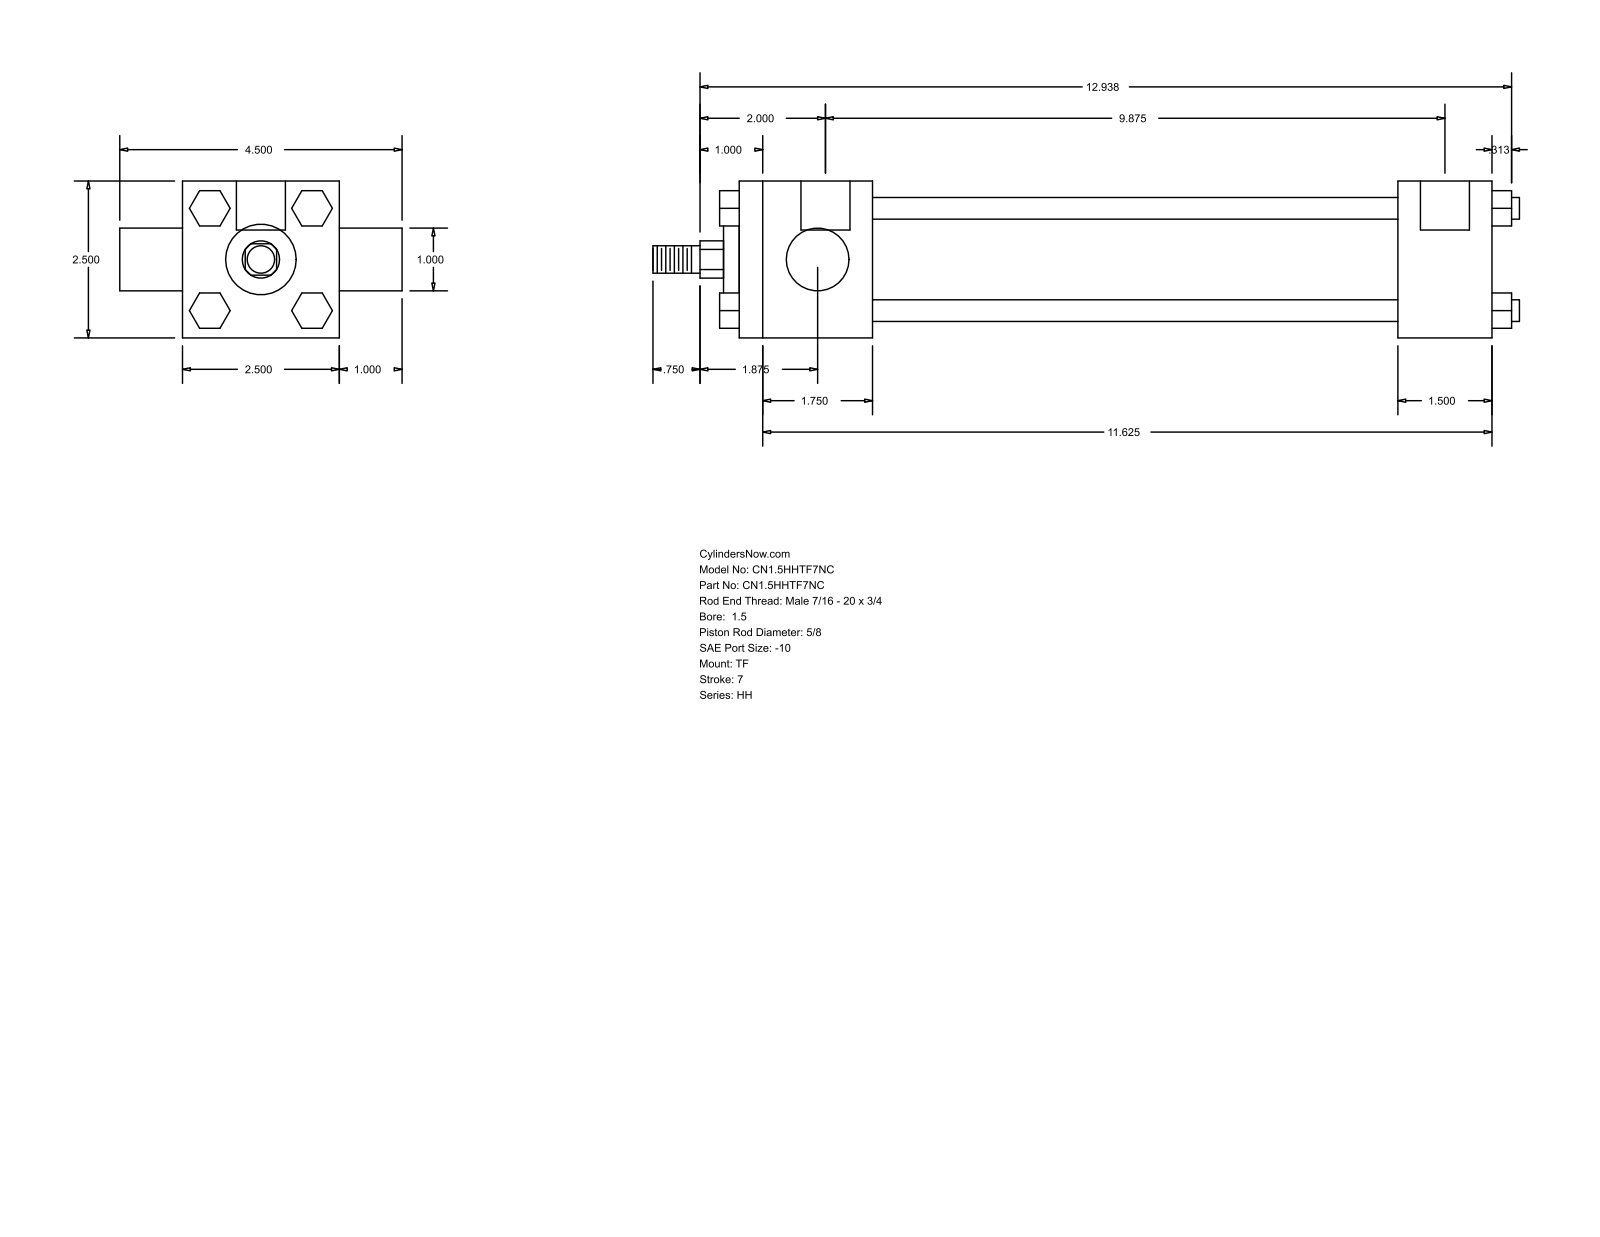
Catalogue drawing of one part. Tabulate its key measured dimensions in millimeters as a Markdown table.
| quantity | value |
| --- | --- |
| part name | HH_TF__0150_0.625 |
| STEP written by | GSSL Pune (CONFIG_CONTROL_DESIGN) |
| units | millimeters |
| bodies | 0 solids, 120 faces (92 planar, 28 cylindrical, 0 other) |
| overall size | 350.84 × 114.3 × 63.5 |
| round holes (diameter × count) | 5.56 × 3, 19.84 × 2 |
| round bosses / shafts (diameter × count) | 8.76 × 4, 44.45 × 1, 28.57 × 1, 25.4 × 1, 15.88 × 1, 11.11 × 1 |
| partial cylindrical surfaces (radius × count) | 7.54 × 1 |
| main face-to-face distances | 63.5, 304.8, 53.97, 250.83, 266.69, 212.72, 38.11, 25.4, 88.9, 20.7 |
| hole center spacings | 1.59, 252.41, 250.82, 254 |
